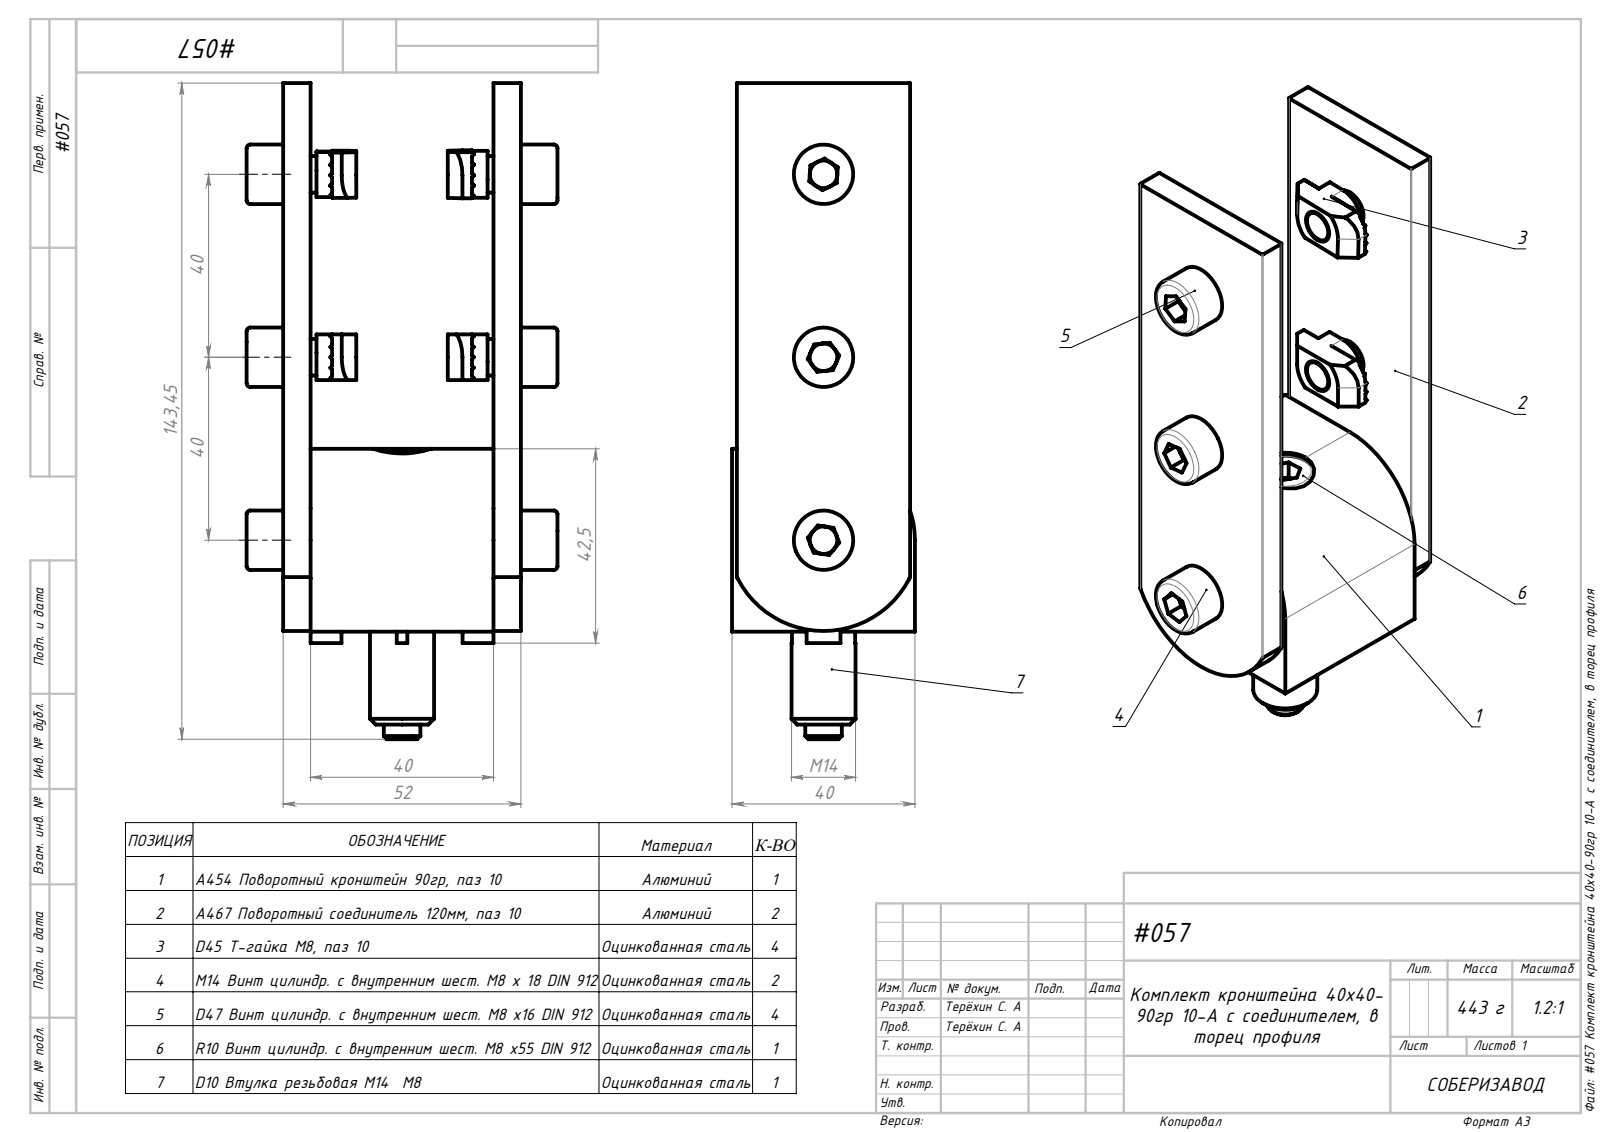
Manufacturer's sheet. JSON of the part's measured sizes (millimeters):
{"part_name": "D45 Т-гайка М8, паз 10_00; R10 Винт цилиндр. с внутренним шест. М8 х55 DIN 912; A454 Поворотный кронштейн 90гр, паз 10; M14 Винт цилиндр. с внутренним шест. М8 х 18 DIN 912 (+4 more)", "step_written_by": "SolidWorks 2021 (AUTOMOTIVE_DESIGN)", "units": "millimeters", "bodies": {"solids": 15, "faces": 476, "planar": 291, "cylindrical": 87, "other": 98}, "overall_size": [143.45, 68, 40], "volume_mm3": 127450, "surface_area_mm2": 45640, "round_holes": [[8.5, 3], [6.7, 2], [7, 1], [7.3, 1], [8.25, 1], [12.7, 1]], "round_bosses_or_shafts": [[13, 4], [8, 4], [14, 1]], "partial_cylinders_radius": [[0.2, 8], [6, 8], [5.67, 4], [20, 1], [21.12, 1]], "face_to_face_distances": [6, 46, 40, 52, 1.05, 38.95, 37.9, 10, 8, 16], "hole_center_spacings": [40, 80]}
